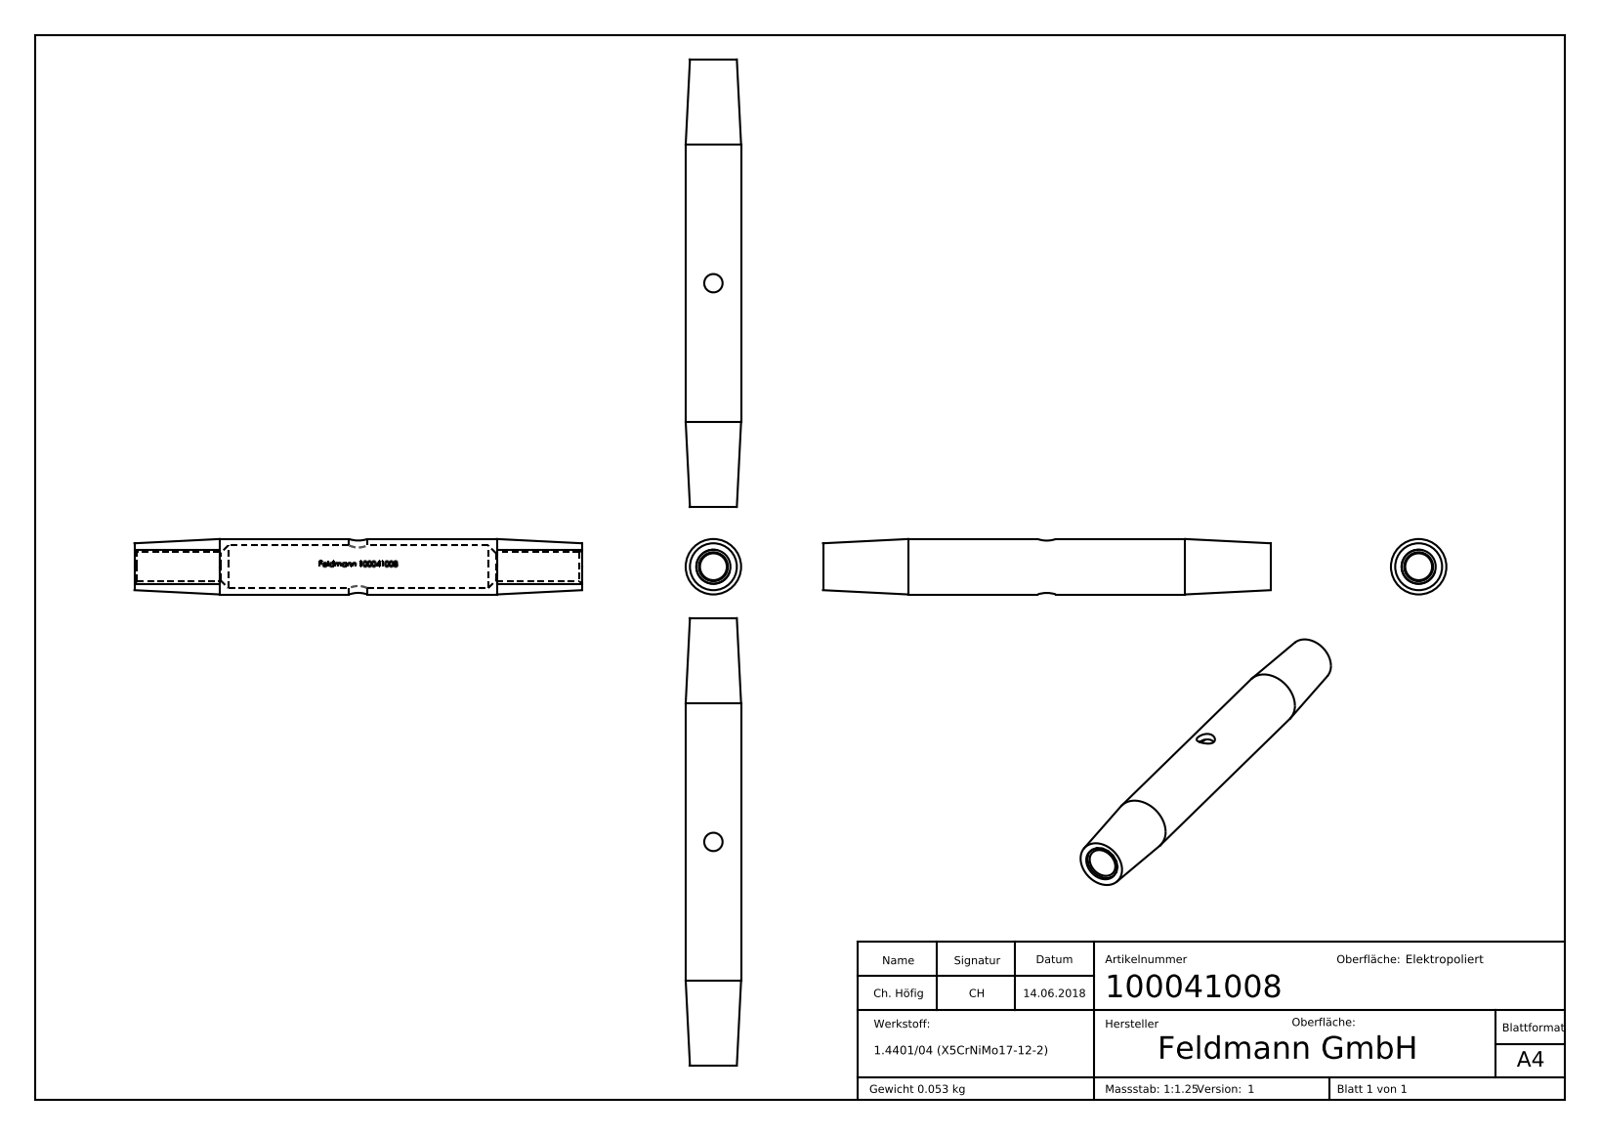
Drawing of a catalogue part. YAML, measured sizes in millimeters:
part_name: "100041008"
step_written_by: "SolidWorks 2015 (CONFIG_CONTROL_DESIGN)"
units: millimeters
bodies: {solids: 1, faces: 253, planar: 81, cylindrical: 46, other: 126}
overall_size: [105, 13, 13]
volume: 6659
surface_area: 7178
round_holes:
  - {diameter: 4.3, count: 1}
  - {diameter: 6.8, count: 1}
  - {diameter: 10, count: 1}
round_bosses_or_shafts:
  - {diameter: 13, count: 1}
partial_cylinders:
  - {radius: 5.1, count: 1}
face_to_face_distances: [105, 0.39, 12.77, 2.02, 14.79, 1.26, 4.29, 11.51, 2.96, 6.36]
